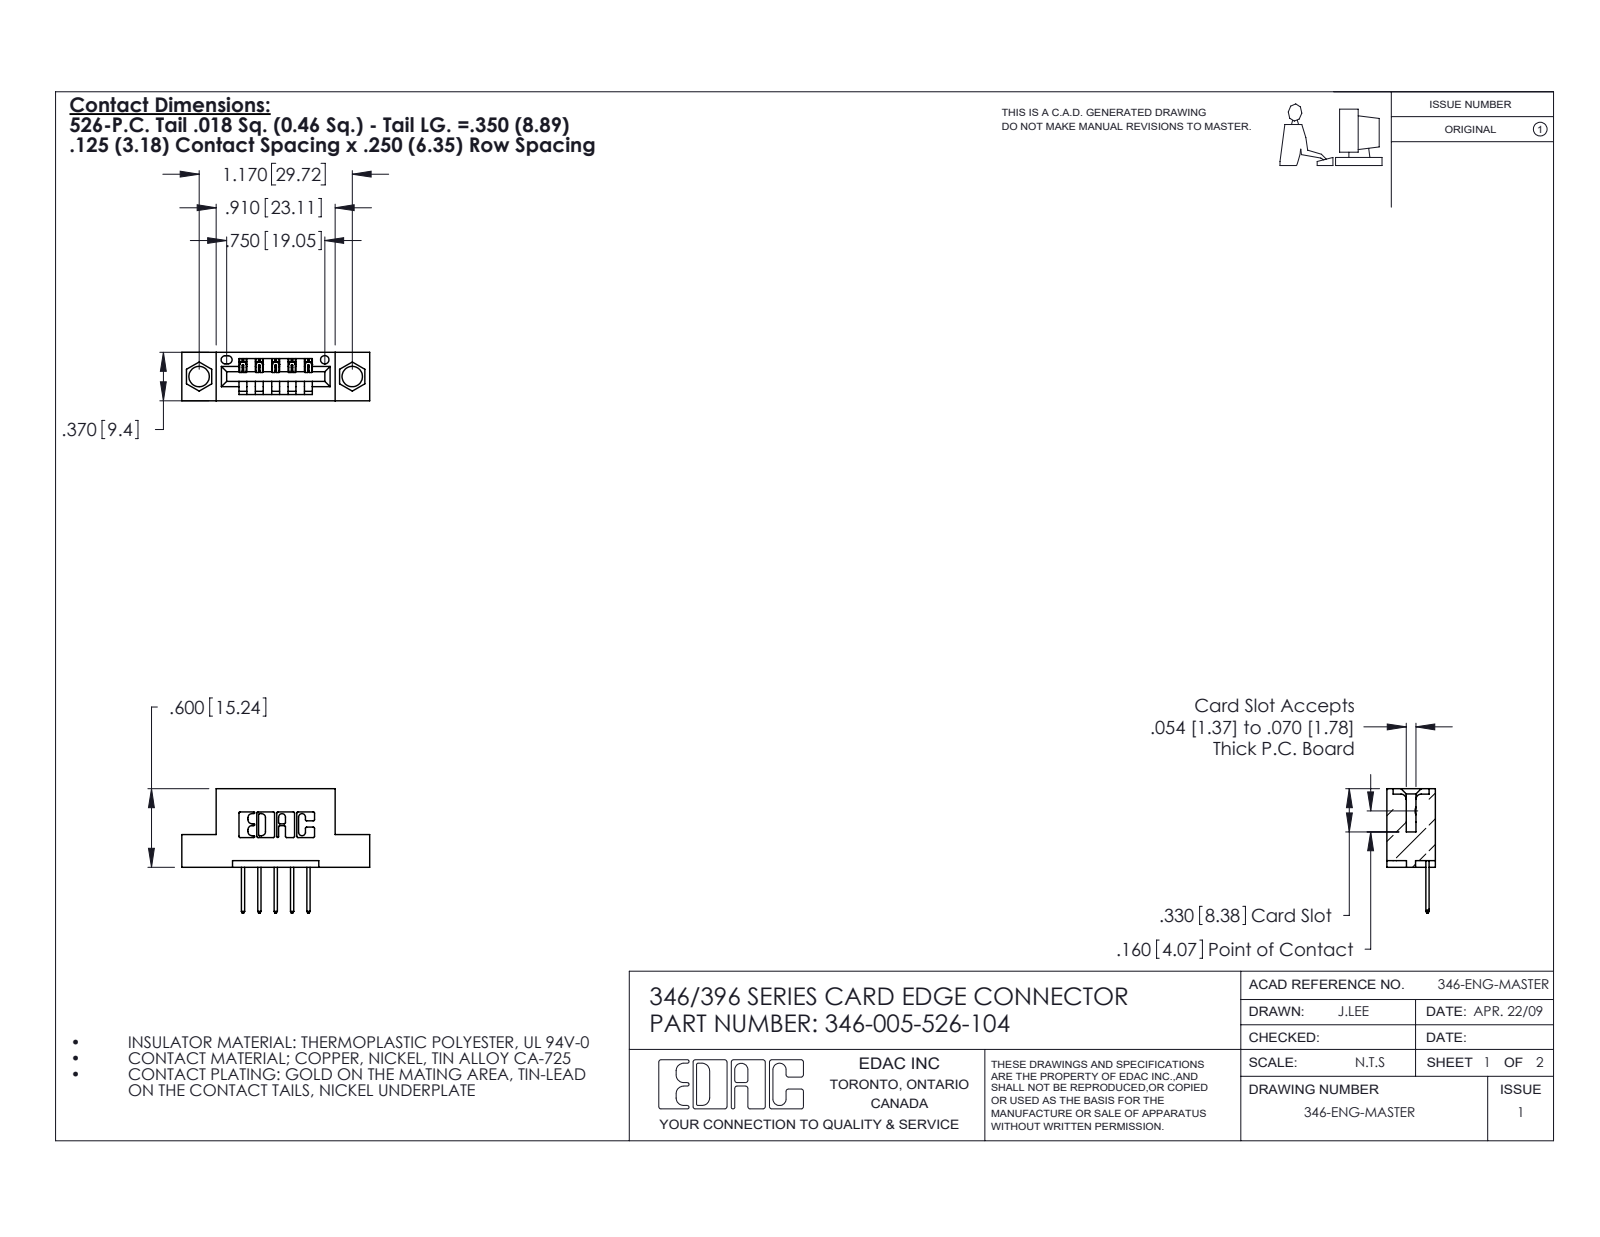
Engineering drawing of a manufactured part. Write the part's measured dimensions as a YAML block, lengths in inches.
part_name: "346-005-526-104; 345-292-001_345-293-126; 346 Part_Flush Mounting Lugs - 0.156 Dia-TH"
step_written_by: "SolidWorks 2020 (CONFIG_CONTROL_DESIGN)"
units: inches
bodies: {solids: 6, faces: 426, planar: 290, cylindrical: 136, other: 0}
overall_size: [1.435, 0.95, 0.37]
volume: 0.191
surface_area: 5.174
round_holes:
  - {diameter: 0.156, count: 2}
  - {diameter: 0.064, count: 1}
partial_cylinders:
  - {radius: 0.01, count: 22}
  - {radius: 0.006, count: 10}
  - {radius: 0.01, count: 10}
  - {radius: 0.007, count: 6}
  - {radius: 0.031, count: 6}
  - {radius: 0.026, count: 3}
  - {radius: 0.031, count: 2}
  - {radius: 0.04, count: 2}
face_to_face_distances: [0.25, 0.37, 0.048, 0.322, 0.148, 0.222, 0.1, 0.174, 0.55, 0.125]
hole_center_spacings: [0.246, 0.969, 1.17]
